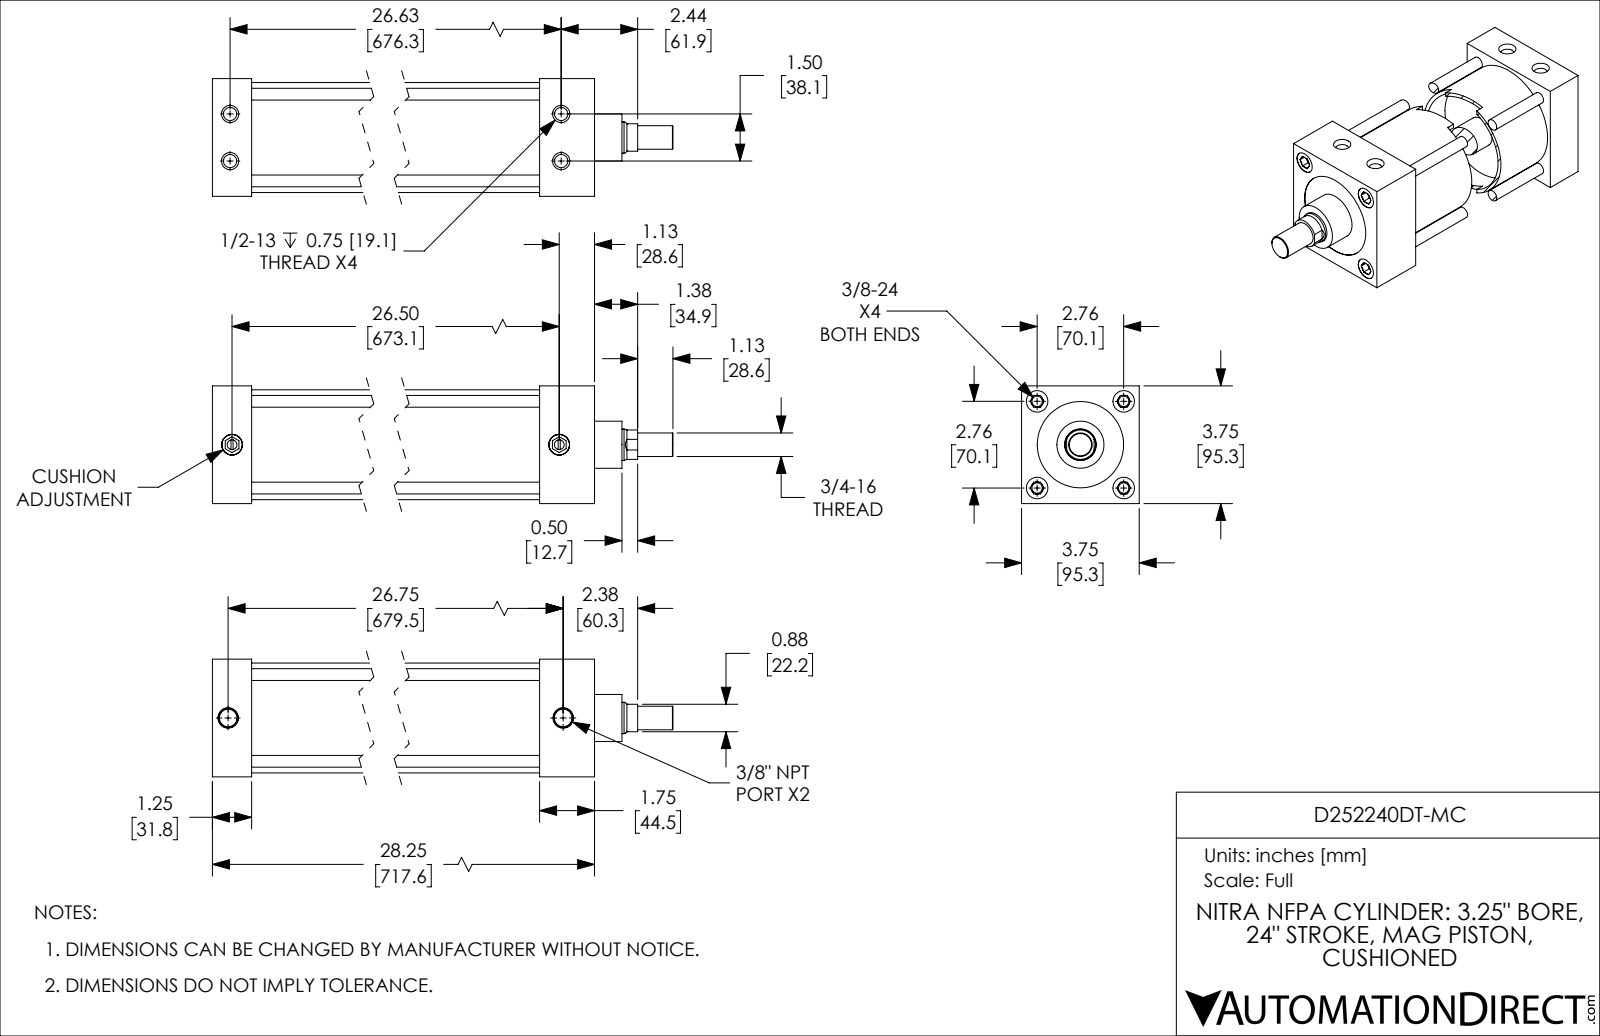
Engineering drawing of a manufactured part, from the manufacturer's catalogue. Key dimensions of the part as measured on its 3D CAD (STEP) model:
Part name (STEP PRODUCT): D252240DT-MC_PISTON_KK1; D252240DT-MC; D252240DT-MC_BODY; D252240DT-MC_CUSHION
STEP written by: SolidWorks 2019 (CONFIG_CONTROL_DESIGN)
Units: inches
Bodies: 4 solids, 246 faces (90 planar, 78 cylindrical, 78 other)
Overall size (bounding box): 30.75 × 3.75 × 3.75
Volume: 116 in³ · Surface area: 903.2 in²
Round holes (diameter × count): ⌀0.332 ×4, ⌀0.422 ×4, ⌀0.687 ×4, ⌀0.312 ×2, ⌀0.562 ×2, ⌀0.656 ×2, ⌀1.001 ×1, ⌀2.75 ×1, ⌀3.251 ×1
Round bosses / shafts (diameter × count): ⌀0.375 ×4, ⌀0.657 ×2, ⌀3.501 ×1, ⌀3.249 ×1, ⌀1.5 ×1, ⌀0.999 ×1, ⌀0.75 ×1
Partial cylindrical surfaces — rounded edges, fillets, slot ends (radius × count): R0.469 ×1
Main face-to-face distances: 1.25, 3.75, 26.5, 25.25, 2.5, 24, 28.25, 27, 25.75, 1.75
Hole centre spacings: 0.753, 1.952, 2.76, 26.698, 1.5, 3.903, 26.625, 26.667
